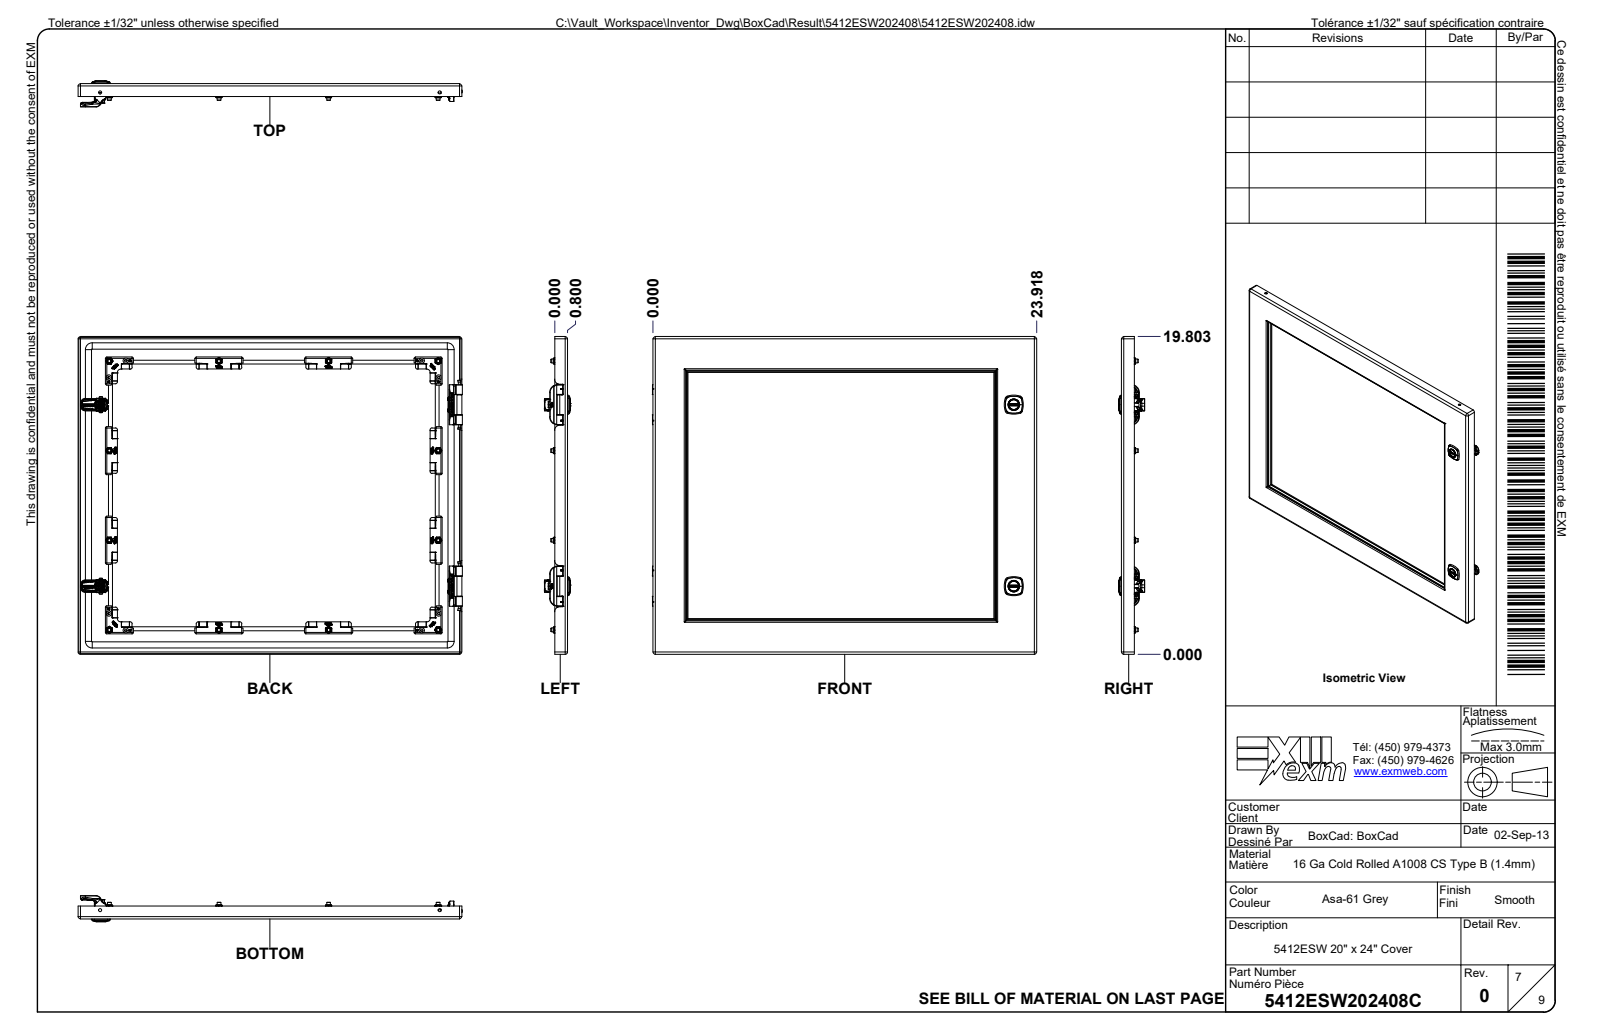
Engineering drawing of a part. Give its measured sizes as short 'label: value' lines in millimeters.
name: 5412ESW202408; 5412ESW202408B; 5412ESW202408B-P; STK-Q-16005 (+8 more)
written by: Autodesk Inventor 2024 (AUTOMOTIVE_DESIGN)
unit: mm
bodies: 101 solids, 15779 faces (6958 planar, 3499 cylindrical, 5322 other)
size: 609.7 × 508 × 236.5
volume: 3 974 000 mm³; area: 3 412 000 mm²
holes: 17× ⌀0.8, 16× ⌀5.1, 16× ⌀7.4, 16× ⌀8, 12× ⌀5, 12× ⌀7, 12× ⌀9.5, 8× ⌀1.1, 8× ⌀4.4, 4× ⌀4.5, 4× ⌀6.9, 4× ⌀9.9
bosses: 17× ⌀5.9, 17× ⌀0.8, 12× ⌀9, 8× ⌀6.9, 8× ⌀1, 4× ⌀18.2, 4× ⌀7.9, 4× ⌀6.7
rounds: 363× R0.5, 139× R0.3, 125× R1, 110× R0.8, 94× R0.2, 68× R2.2, 54× R0.4, 50× R0.3
face distances: 1.3, 23.5, 22.2, 26.2, 24.9, 2.7, 506.7, 230.7, 216.1, 214.8
hole spacings: 287.1, 459.5, 8.9, 18.7, 26.1, 26.7, 35.2, 40.4
